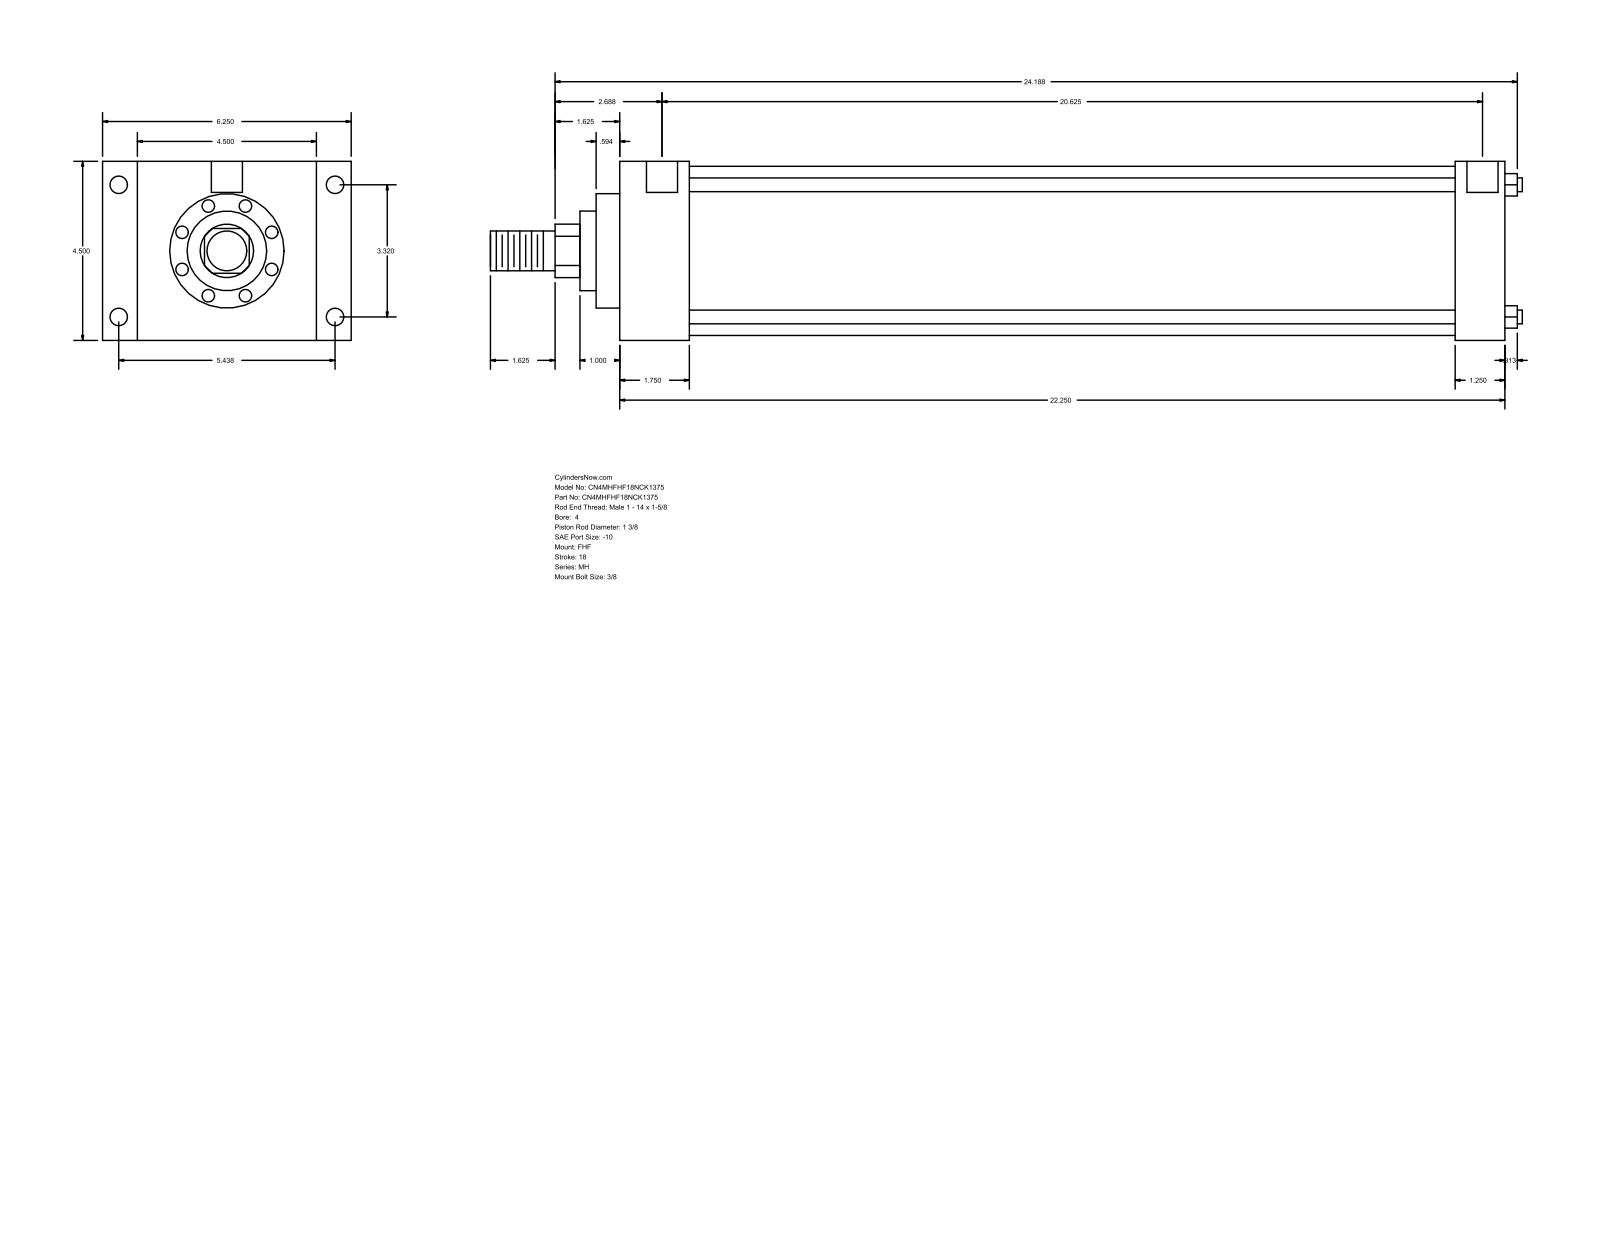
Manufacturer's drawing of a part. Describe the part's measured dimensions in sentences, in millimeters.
The part is named "MH_FHF__0400_1.375". Its 3-D file was written by "GSSL Pune (CONFIG_CONTROL_DESIGN)". It is 0 solids with 90 faces: 61 planar, 29 cylindrical and 0 other. Overall it measures 658.81 by 158.75 by 114.3 millimeters. Round holes: 4 of diameter 8.73, 4 of diameter 11.13, 2 of diameter 19.84. Round bosses or shafts: 4 of diameter 8.76, 1 of diameter 107.95, 1 of diameter 73.03, 1 of diameter 50.8, 1 of diameter 34.92, 1 of diameter 25.4. Partial cylindrical surfaces (rounded edges, fillets, slot ends): 1 of radius 17.06. The main face-to-face distances are 114.3, 565.15, 44.45, 520.7, 22.23, 136.53, 158.76, 533.4, 488.95, 31.75. The hole center spacings are 1.59, 84.32, 138.12, 161.82, 525.47, 527.06, 523.88.
